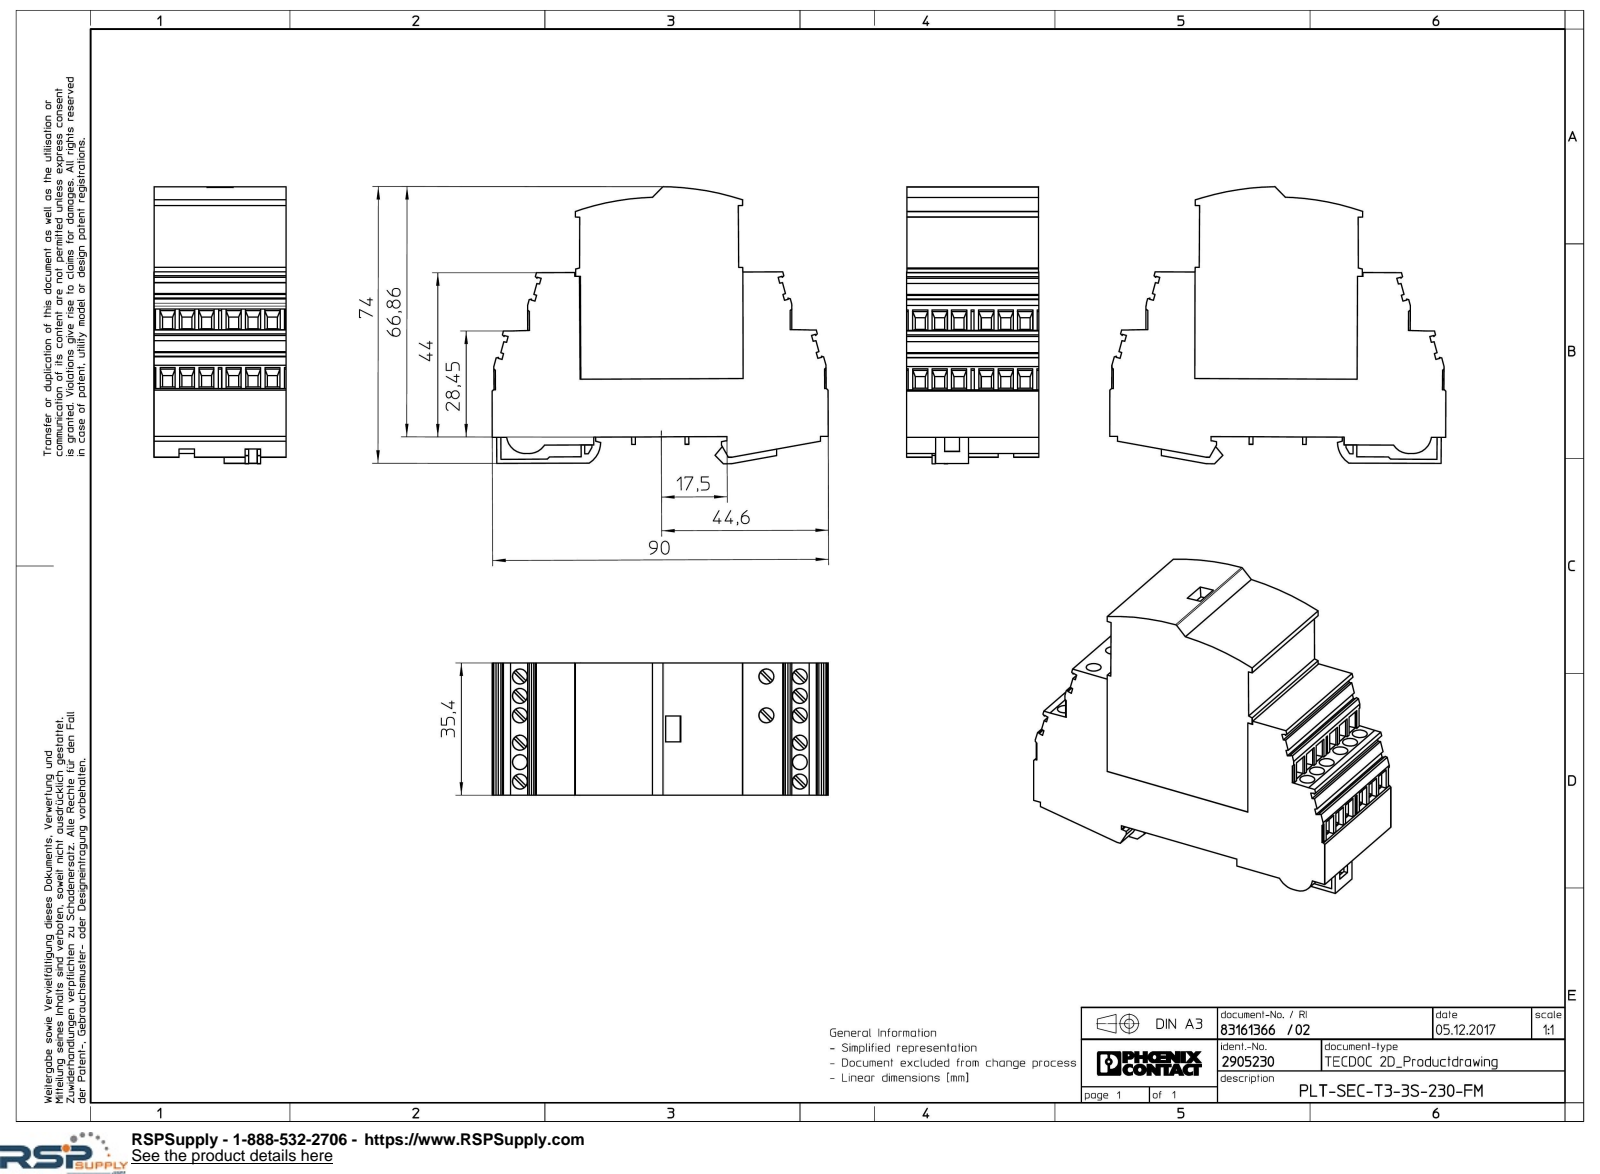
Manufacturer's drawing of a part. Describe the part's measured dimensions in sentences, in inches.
The part is named "PLT_SEC_T3_3S_230_FM-select". Its 3-D file was written by "Creo Elements/Direct Modeling 20.1A 29-Sep-2018 (C) Parametric Technology GmbH (AUTOMOTIVE_DESIGN)". It is 3 solids with 687 faces: 652 planar, 11 cylindrical and 24 other. Overall it measures 3.543 by 2.917 by 1.394 inches. Its volume is 9.784 cubic inches and its surface area 41.32 square inches. Round holes: 2 of diameter 0.157. Partial cylindrical surfaces (rounded edges, fillets, slot ends): 2 of radius 0.197, 1 of radius 0.02, 1 of radius 0.118, 1 of radius 0.256, 1 of radius 2.717, 1 of radius 2.827. The main face-to-face distances are 1.394, 1.392, 1.393, 1.391, 1.732, 0.176, 0.083, 1.815, 2.658, 0.885. The hole center spacings are 0.409.
